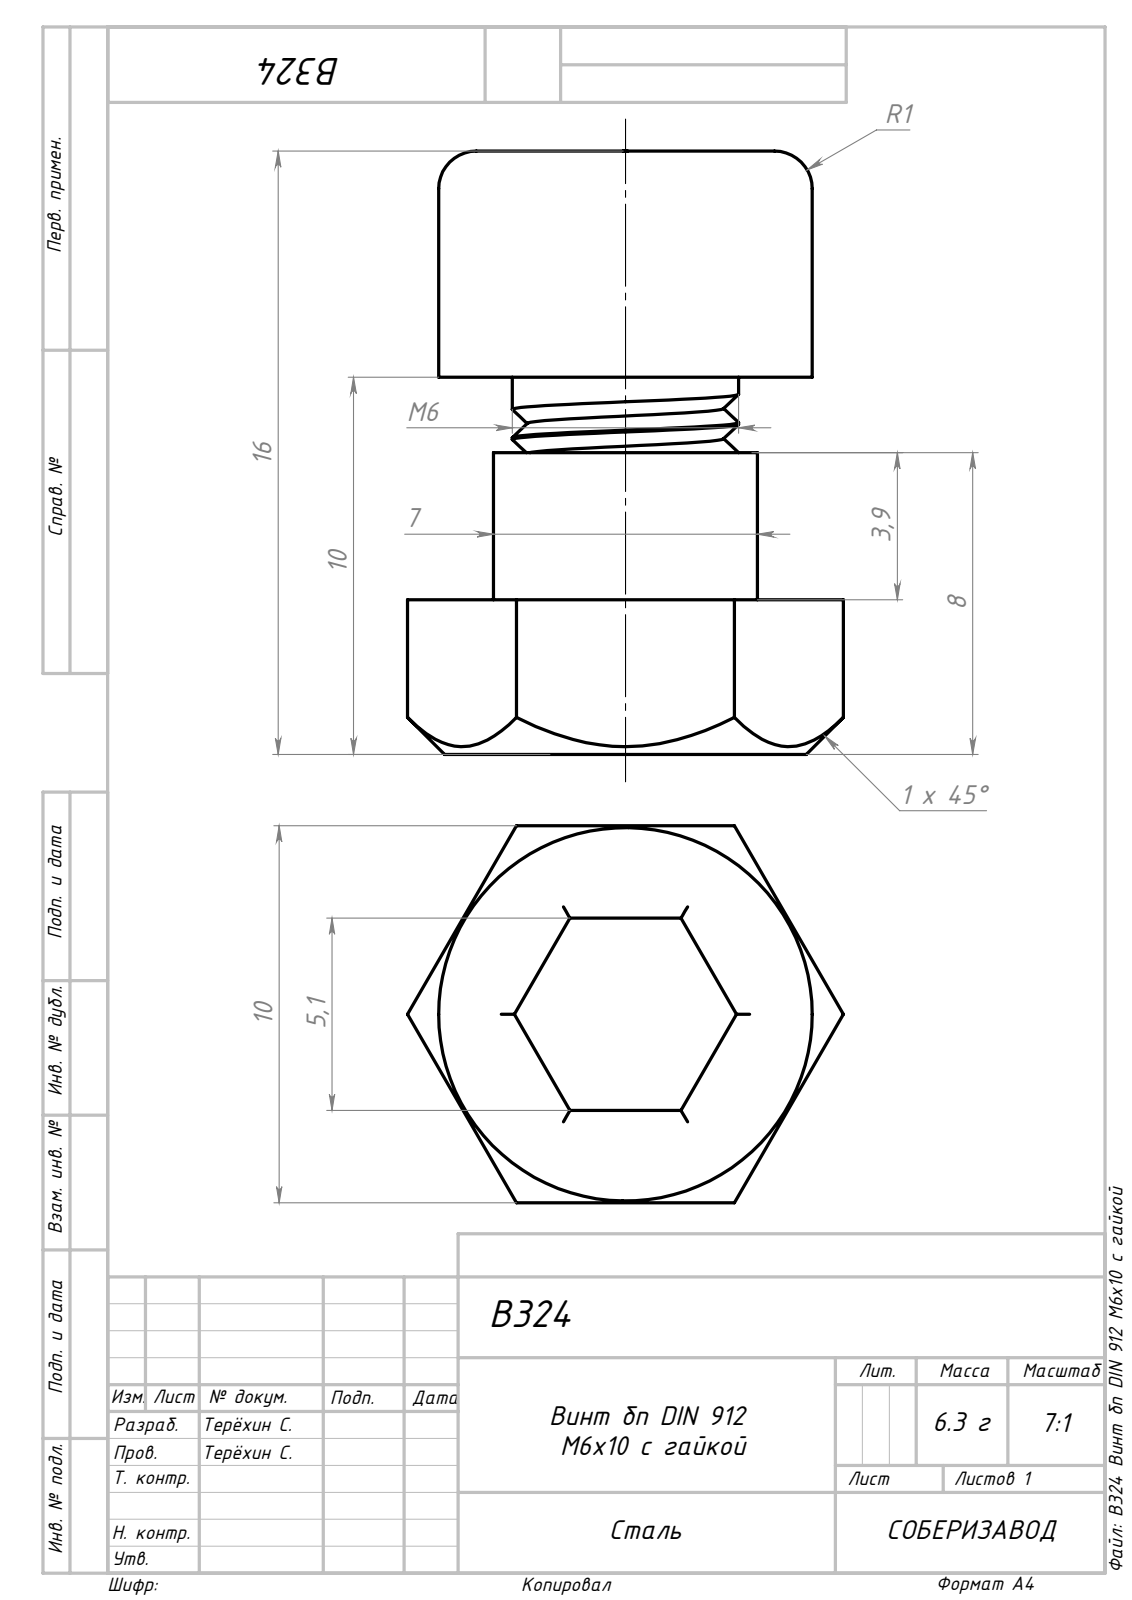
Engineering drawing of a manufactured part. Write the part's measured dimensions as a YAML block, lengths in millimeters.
part_name: "B324 Винт бп DIN 912 М6х10 с гайкой"
step_written_by: "SolidWorks 2022 (AUTOMOTIVE_DESIGN)"
units: millimeters
bodies: {solids: 2, faces: 95, planar: 20, cylindrical: 48, other: 27}
overall_size: [16, 11.55, 10]
volume: 909
surface_area: 1144
round_holes:
  - {diameter: 5.3, count: 1}
round_bosses_or_shafts:
  - {diameter: 9.9, count: 1}
  - {diameter: 7, count: 1}
  - {diameter: 6, count: 1}
partial_cylinders:
  - {radius: 0.3, count: 6}
face_to_face_distances: [10, 2.45, 7.55, 4.1, 5.9, 5.1, 2, 4, 12, 7.9]
